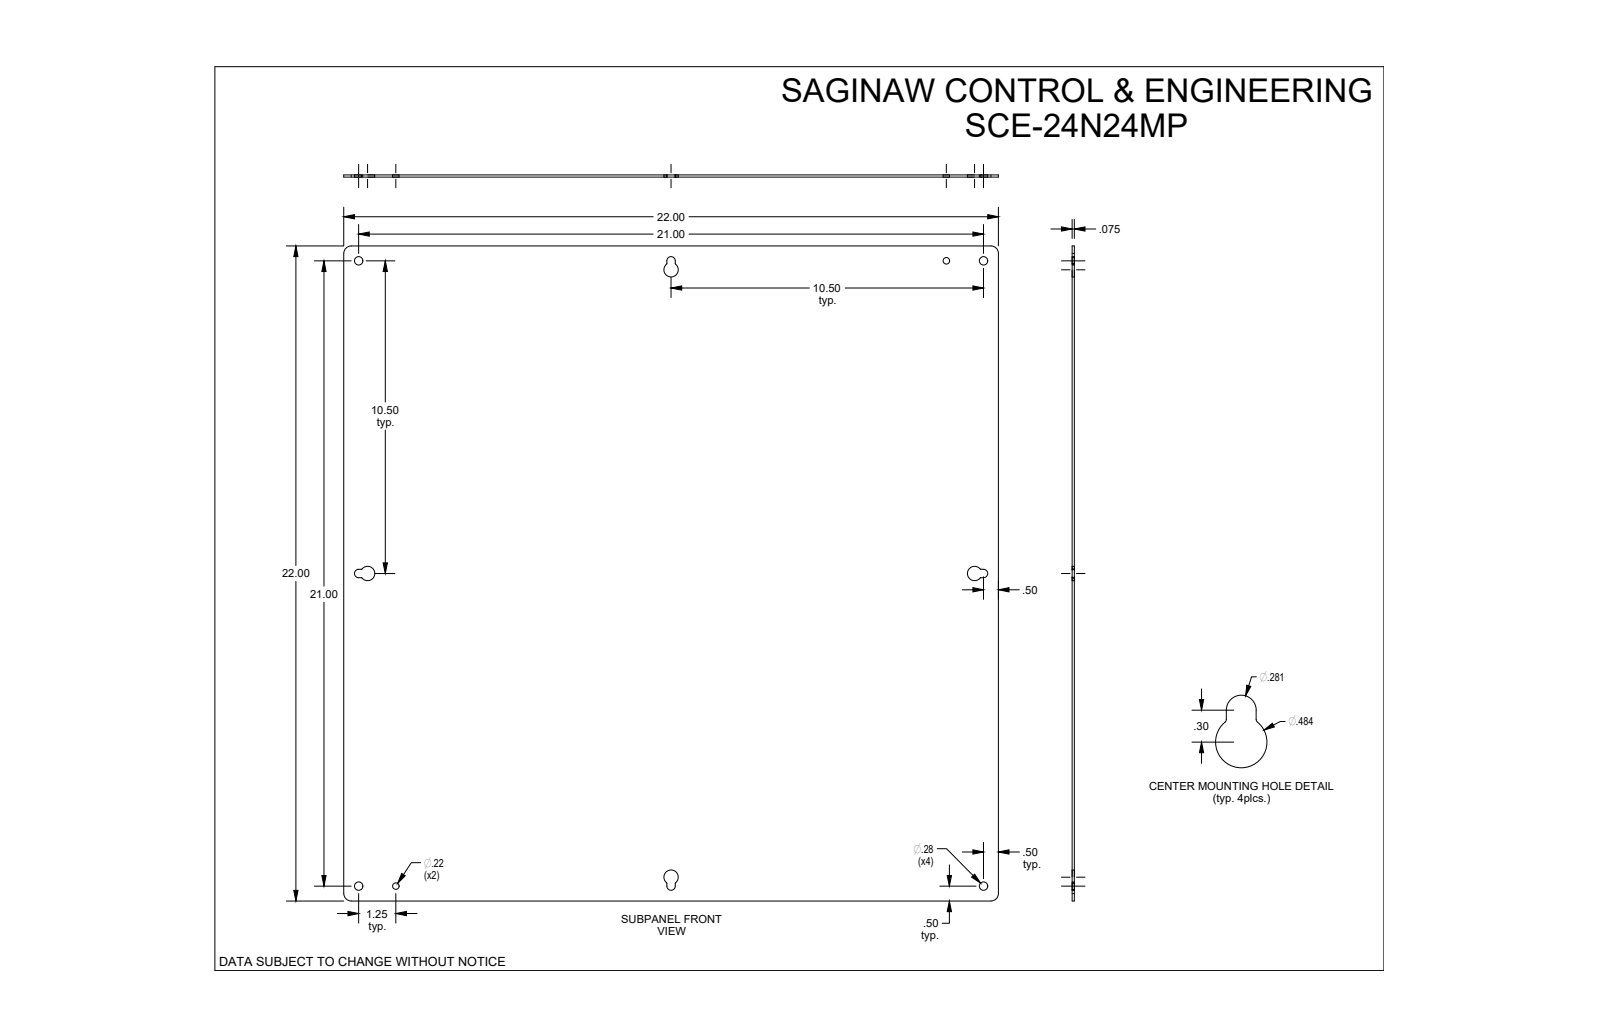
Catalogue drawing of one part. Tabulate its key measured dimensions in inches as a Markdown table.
| quantity | value |
| --- | --- |
| part name | SCE-24N24MP |
| STEP written by | SolidWorks 2019 (CONFIG_CONTROL_DESIGN) |
| units | inches |
| bodies | 1 solid, 40 faces (14 planar, 26 cylindrical, 0 other) |
| overall size | 22 × 22 × 0.075 |
| volume | 36.2 in³ |
| surface area | 972.9 in² |
| round holes (diameter × count) | 0.281 × 4, 0.218 × 2 |
| partial cylindrical surfaces (radius × count) | 0.03 × 8, 0.141 × 4, 0.242 × 4, 0.25 × 4 |
| main face-to-face distances | 0.075, 22, 10.859, 11.141, 0.281 |
| hole center spacings | 21, 1.25, 19.75, 21.037, 28.828, 29.698, 27.987 |
